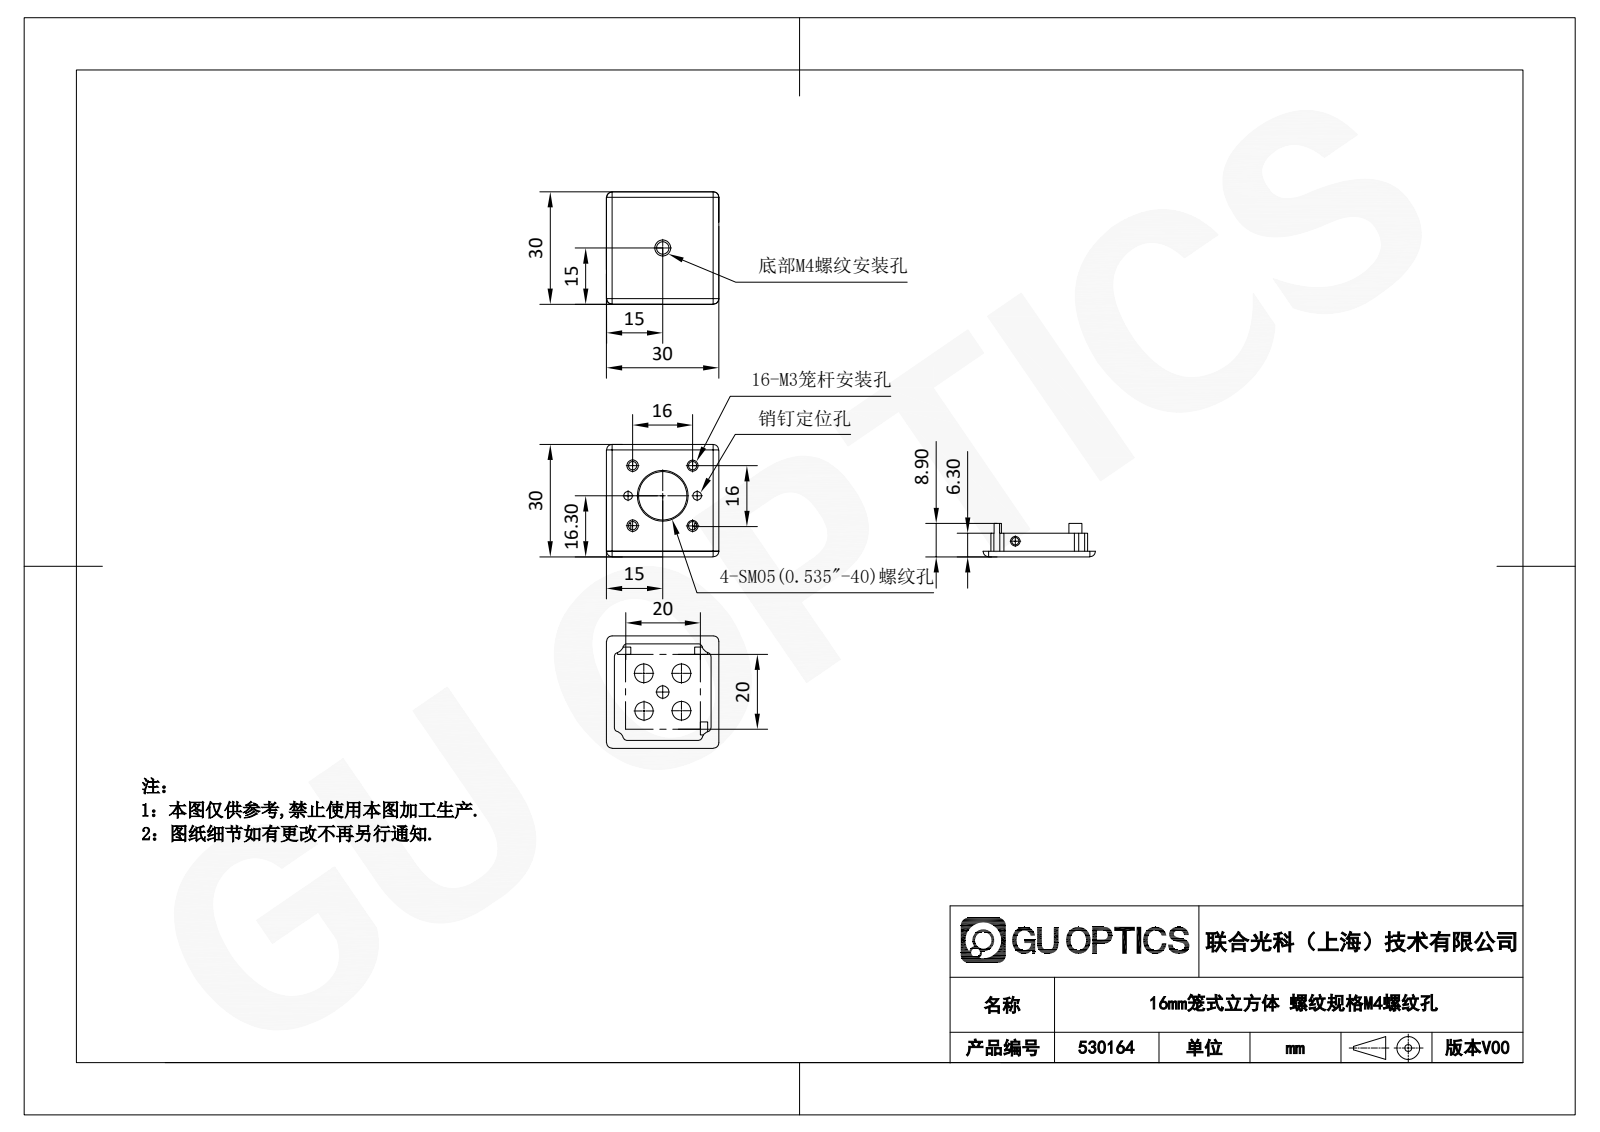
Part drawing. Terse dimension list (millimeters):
name: 530164
written by: SolidWorks 2020 (CONFIG_CONTROL_DESIGN)
unit: mm
bodies: 4 solids, 161 faces (55 planar, 67 cylindrical, 39 other)
size: 30 × 30 × 30
volume: 11 050 mm³; area: 9 836 mm²
holes: 8× ⌀2.26, 4× ⌀2.4, 4× ⌀5, 2× ⌀2.05, 2× ⌀2.9, 2× ⌀12.96, 1× ⌀3.3
bosses: 2× ⌀2.5
rounds: 12× R1.5, 8× R1.2, 4× R2.5, 4× R3
face distances: 2.1, 27.9, 30, 25.8, 2, 28, 6.3, 21.7, 23.7, 26.5
hole spacings: 8.09, 11.31, 16, 18.97, 7.07, 9.2, 10, 22.63
